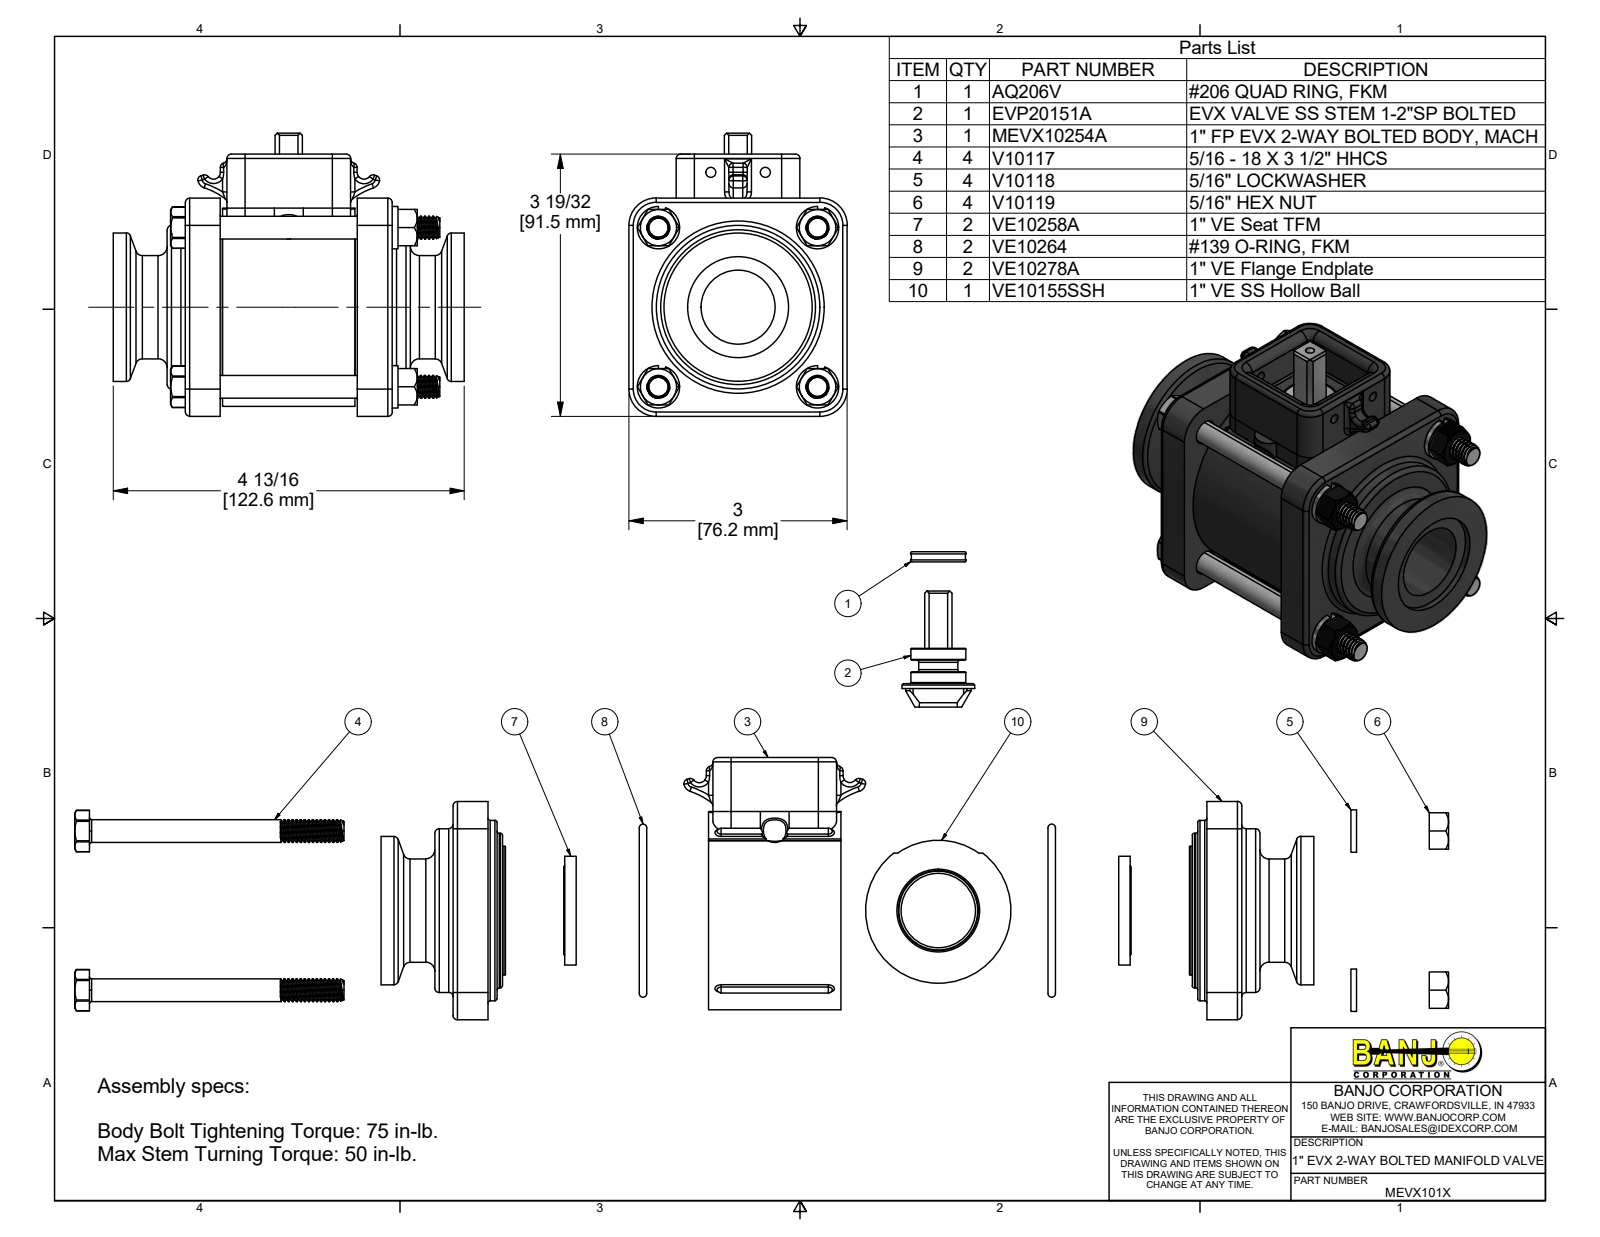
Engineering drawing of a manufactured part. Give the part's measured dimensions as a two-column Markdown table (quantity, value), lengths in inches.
| quantity | value |
| --- | --- |
| part name | MEVX101X; MEVX10254A; MEVX10254AX; VE10155SSH (+8 more) |
| STEP written by | Autodesk Inventor 2019 (AUTOMOTIVE_DESIGN) |
| units | inches |
| bodies | 22 solids, 1313 faces (222 planar, 520 cylindrical, 571 other) |
| overall size | 4.825 × 3.893 × 3 |
| volume | 20 in³ |
| surface area | 185.4 in² |
| round holes (diameter × count) | 0.252 × 4, 0.322 × 4, 0.35 × 4, 1.02 × 3, 0.135 × 2, 0.76 × 1, 1.39 × 1, 1.5 × 1, 2.12 × 1, 2.375 × 1, 2.5 × 1 |
| round bosses / shafts (diameter × count) | 0.268 × 60, 0.583 × 4, 0.313 × 4, 2.725 × 1, 2.48 × 1, 2.25 × 1, 2.124 × 1, 2.04 × 1 |
| partial cylindrical surfaces (radius × count) | 0.06 × 42, 0.03 × 12, 0.062 × 8, 0.134 × 8, 0.375 × 8, 0.125 × 6, 0.21 × 4, 0.25 × 4 |
| main face-to-face distances | 0.48, 2.365, 2.845, 3, 0.99, 1.47, 3.355, 3.835, 1.885, 0.605 |
| hole center spacings | 1.547, 2.188, 1.891, 3.094, 3.294, 0.75, 1.046, 1.046 |
